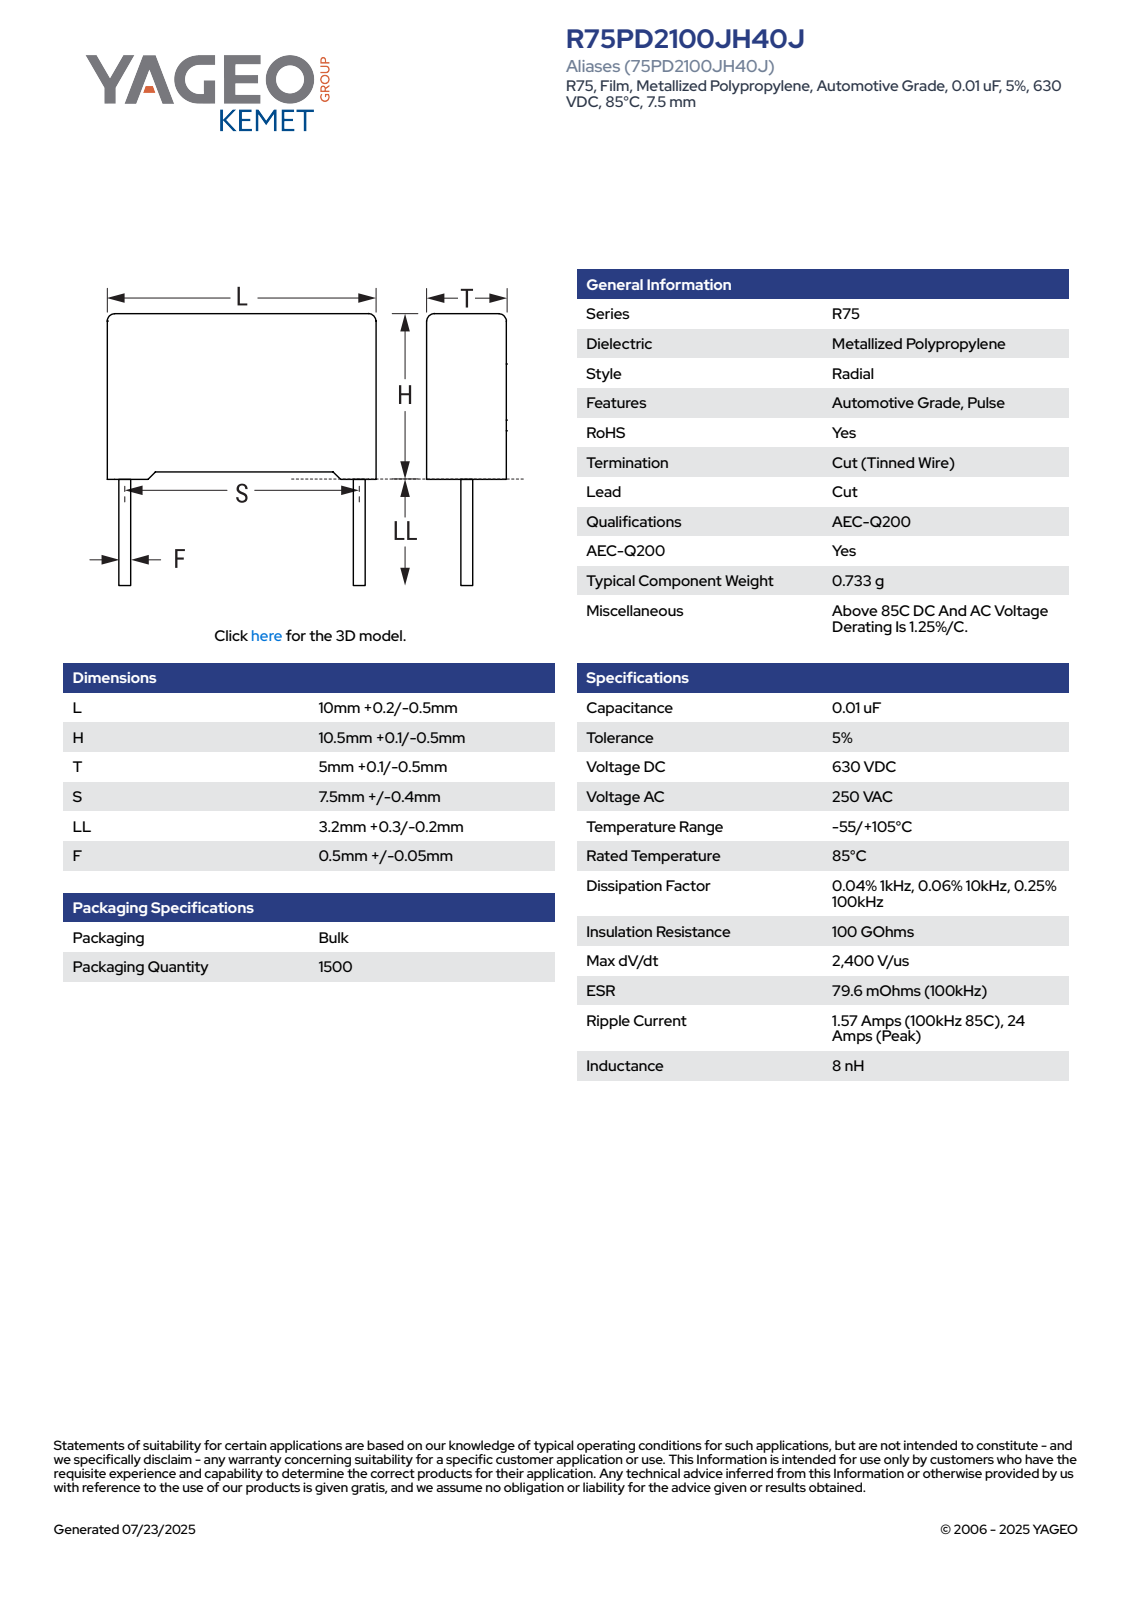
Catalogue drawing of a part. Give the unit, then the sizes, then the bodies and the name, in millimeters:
Units: millimetres
Overall size (bounding box): 14.1 × 10.2 × 5.11
Round bosses / shafts (diameter × count): ⌀0.55 ×2
Partial cylindrical surfaces — rounded edges, fillets, slot ends (radius × count): R0.5 ×4
Main face-to-face distances: 5.1, 10.2, 9.85, 0.34, 4.76, 0.75, 10.6, 9.86, 4.42, 9.52
Volume: 519 mm³ · Surface area: 459 mm²
Bodies: 4 solids, 85 faces (77 planar, 8 cylindrical, 0 other)
Part name (STEP PRODUCT): CFR_RB2_10X10.5X5_L10.2H10.6T5.1S7.5LL3.5F0.55
STEP written by: SolidWorks 2021 (AUTOMOTIVE_DESIGN)
